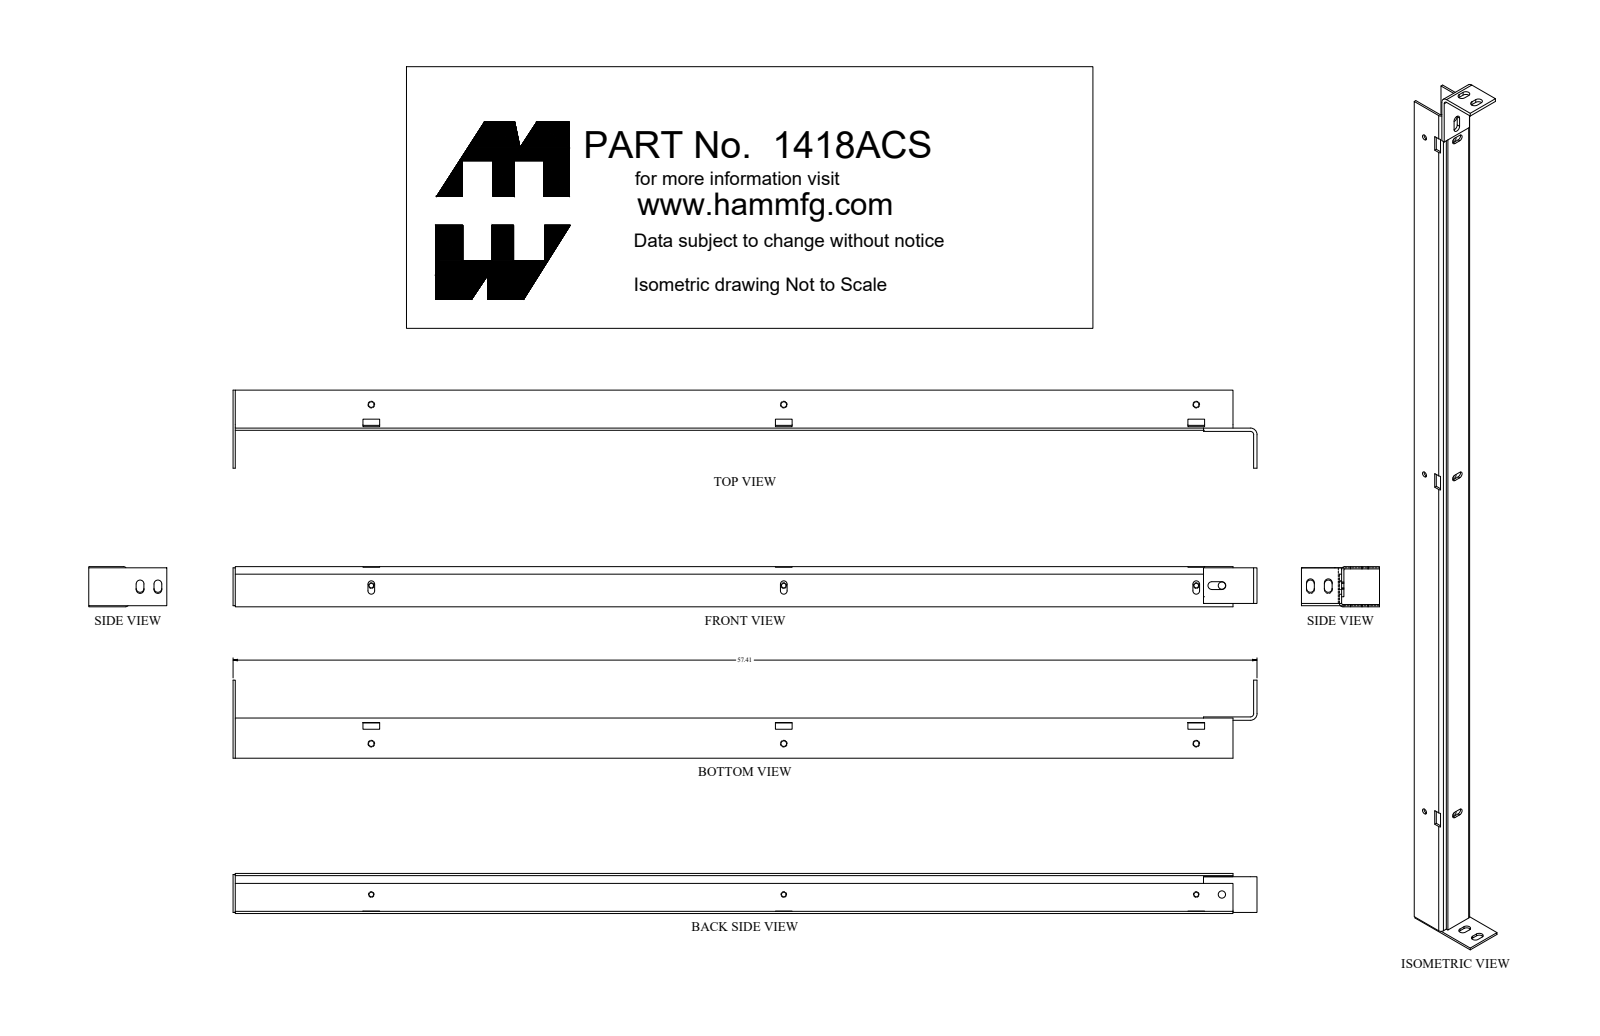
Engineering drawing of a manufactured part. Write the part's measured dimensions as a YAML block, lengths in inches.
part_name: "1418ACS"
step_written_by: "SolidWorks 2019 (AUTOMOTIVE_DESIGN)"
units: inches
bodies: {solids: 4, faces: 104, planar: 72, cylindrical: 32, other: 0}
overall_size: [57.438, 4.375, 2.248]
volume: 54.11
surface_area: 904.3
round_holes:
  - {diameter: 0.283, count: 3}
  - {diameter: 0.344, count: 3}
  - {diameter: 0.406, count: 1}
partial_cylinders:
  - {radius: 0.219, count: 8}
  - {radius: 0.06, count: 3}
  - {radius: 0.185, count: 3}
  - {radius: 0.187, count: 3}
  - {radius: 0.188, count: 3}
  - {radius: 0.25, count: 2}
face_to_face_distances: [0.125, 0.125, 2.123, 2.248, 1.998, 2.123, 0.25, 2.125, 2, 2.25]
hole_center_spacings: [23.125, 23.125, 46.25, 1.438, 24.563, 47.688]
